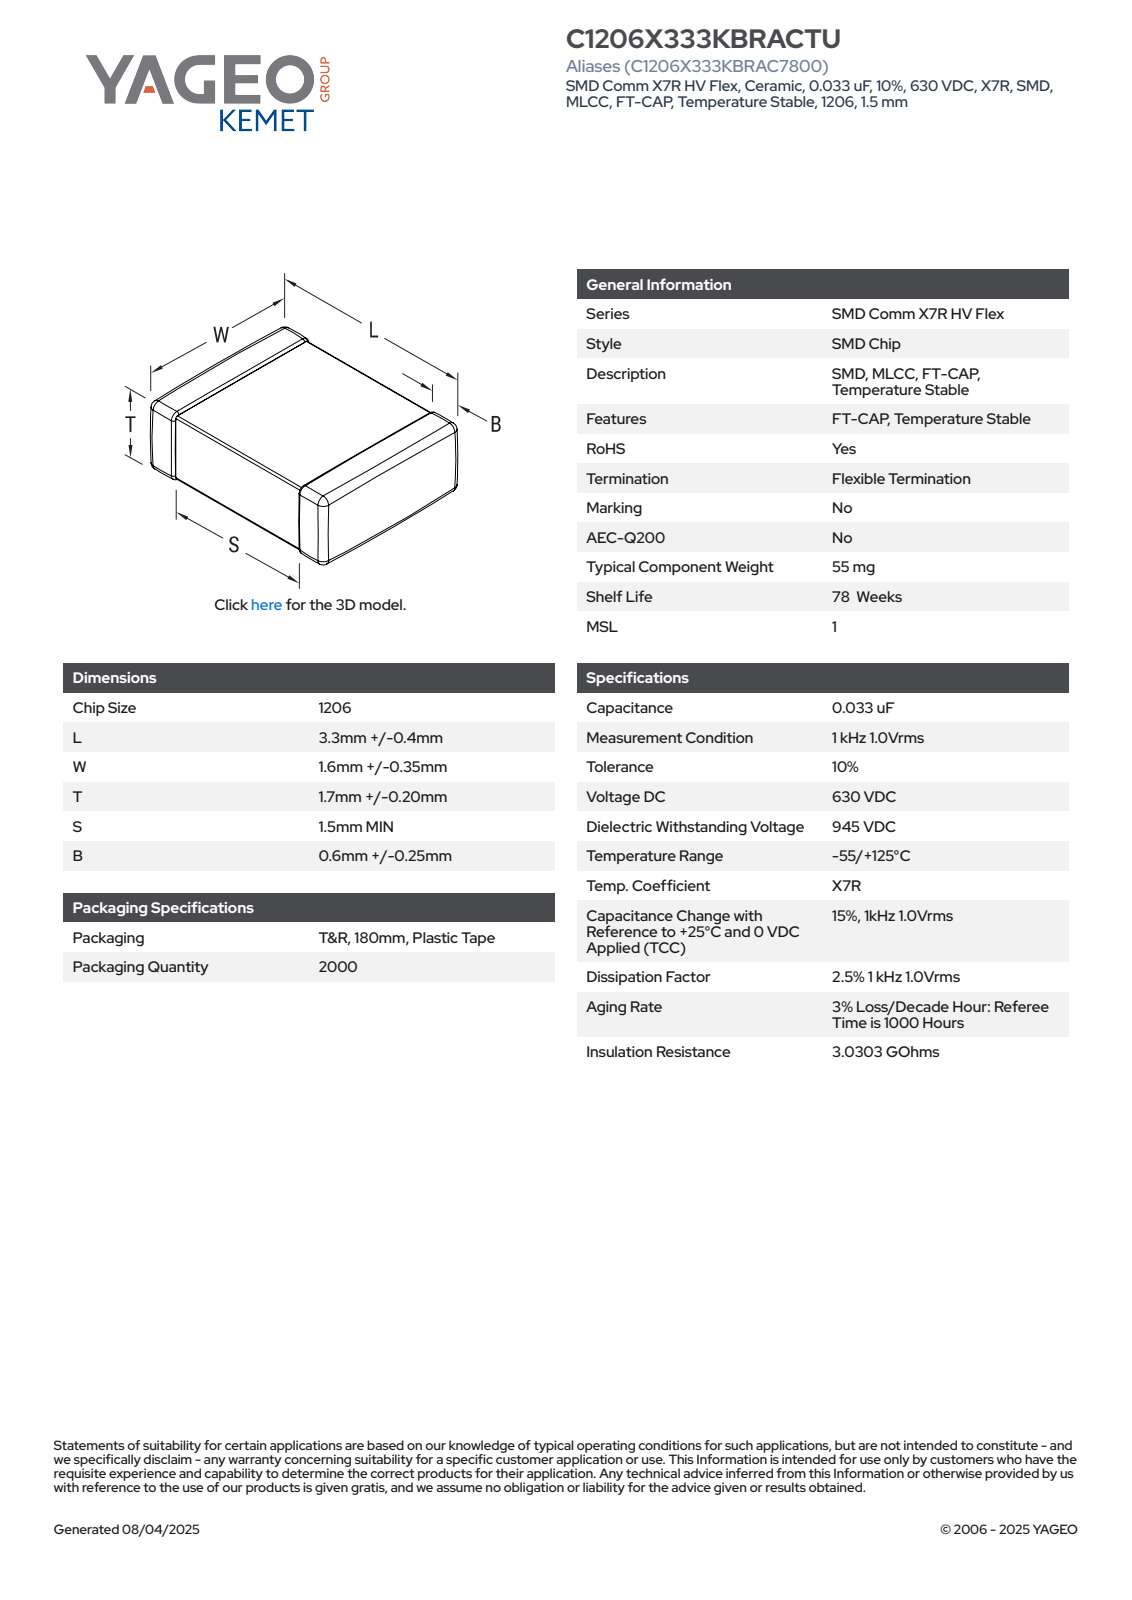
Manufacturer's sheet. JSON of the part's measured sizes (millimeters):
{"part_name": "CCS_CCSTDNOS_1206_L3.7W1.95T1.9B0.85", "step_written_by": "SolidWorks 2014 (AUTOMOTIVE_DESIGN)", "units": "millimeters", "bodies": {"solids": 4, "faces": 121, "planar": 71, "cylindrical": 34, "other": 16}, "overall_size": [3.7, 1.95, 1.9], "volume_mm3": 13, "surface_area_mm2": 36, "face_to_face_distances": [1.86, 1.91, 1.82, 1.87, 3.7, 1.9, 1.95, 0.86, 0.82, 1.05]}
